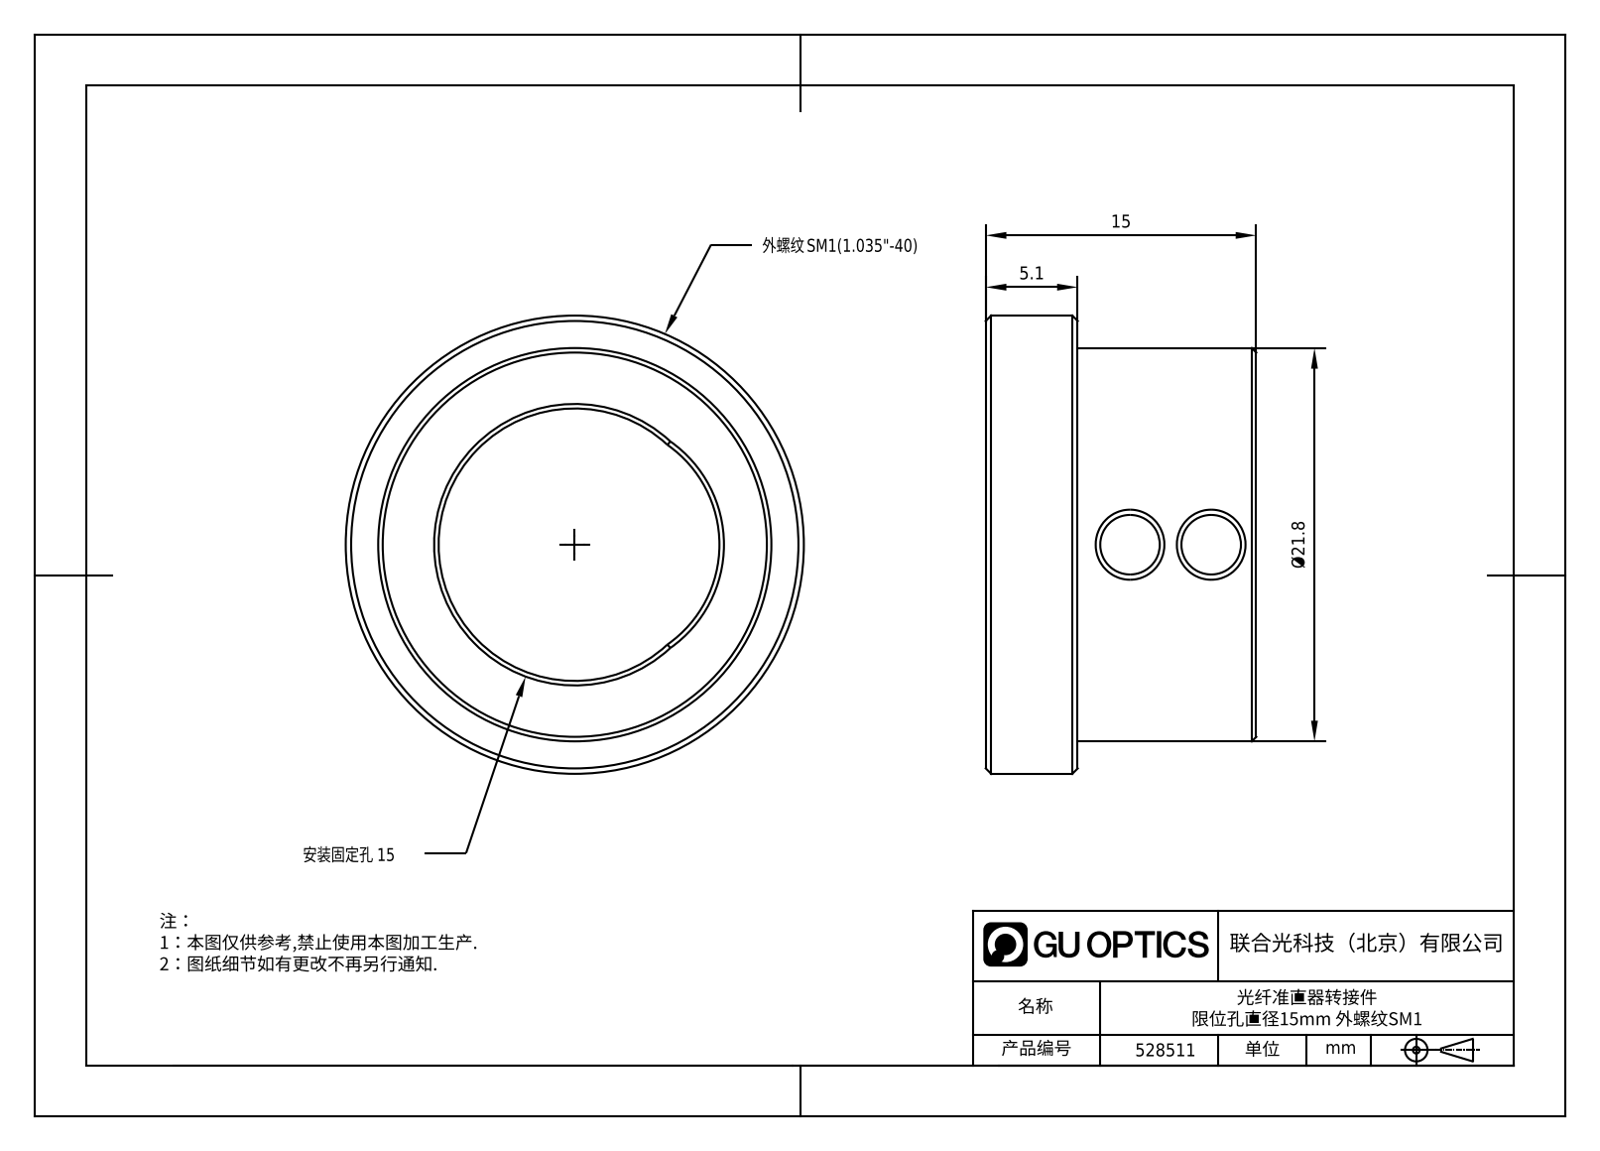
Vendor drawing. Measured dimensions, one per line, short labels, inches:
written by: SolidWorks 2016 (AUTOMOTIVE_DESIGN)
unit: in
bodies: 1 solid, 47 faces (9 planar, 20 cylindrical, 18 other)
size: 1 × 1 × 0.591
volume: 0.211 in³; area: 3.81 in²
holes: 2× ⌀0.05, 2× ⌀0.13
bosses: 1× ⌀1, 1× ⌀0.858
rounds: 1× R0.266, 1× R0.297
face distances: 0.591, 0.201, 0.39, 0.05, 0.151, 0.101, 0.541, 0.44
hole spacings: 0.177, 0.799
